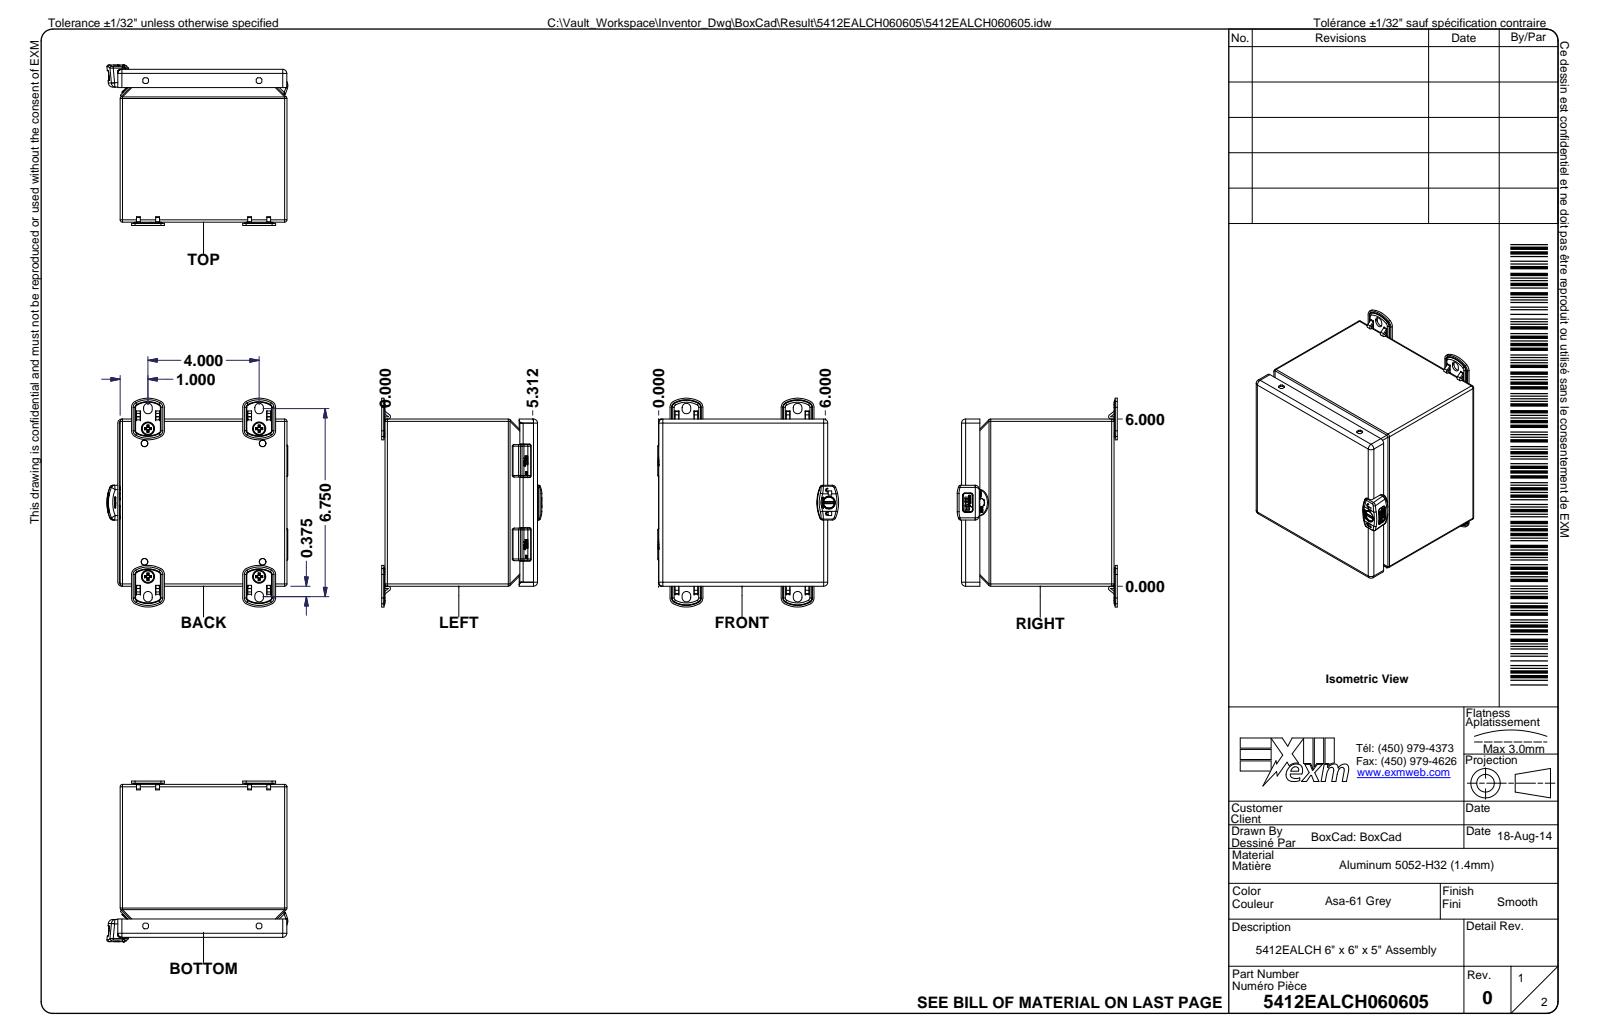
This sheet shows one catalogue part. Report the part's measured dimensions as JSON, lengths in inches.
{"part_name": "5412EALCH060605; 5412EALCH060605B; 5412EALCH060605B-P; STK-A-70469-1 (+8 more)", "step_written_by": "Autodesk Inventor 2020 (AUTOMOTIVE_DESIGN)", "units": "inches", "bodies": {"solids": 51, "faces": 6818, "planar": 2990, "cylindrical": 1592, "other": 2236}, "overall_size": [7.496, 6.503, 5.76], "volume_in3": 16.06, "surface_area_in2": 576.7, "round_holes": [[0.197, 4], [0.197, 4], [0.236, 4], [0.32, 4], [0.165, 3], [0.173, 3], [0.236, 3], [0.03, 2], [0.175, 2], [0.201, 2], [0.24, 2], [0.394, 2]], "round_bosses_or_shafts": [[0.232, 8], [0.236, 5], [0.5, 4], [0.3, 3], [0.197, 3], [0.193, 3], [0.394, 2], [0.035, 2]], "partial_cylinders_radius": [[0.02, 213], [0.01, 152], [0.039, 78], [0.008, 60], [0.059, 55], [0.004, 54], [0.031, 33], [0.084, 24]], "face_to_face_distances": [0.053, 5.947, 6, 5.894, 0.053, 5.433, 5.38, 5.486, 5.433, 0.236], "hole_center_spacings": [4.25, 4.25, 0.546, 4.159, 4.782, 3, 6.01, 6.314]}
